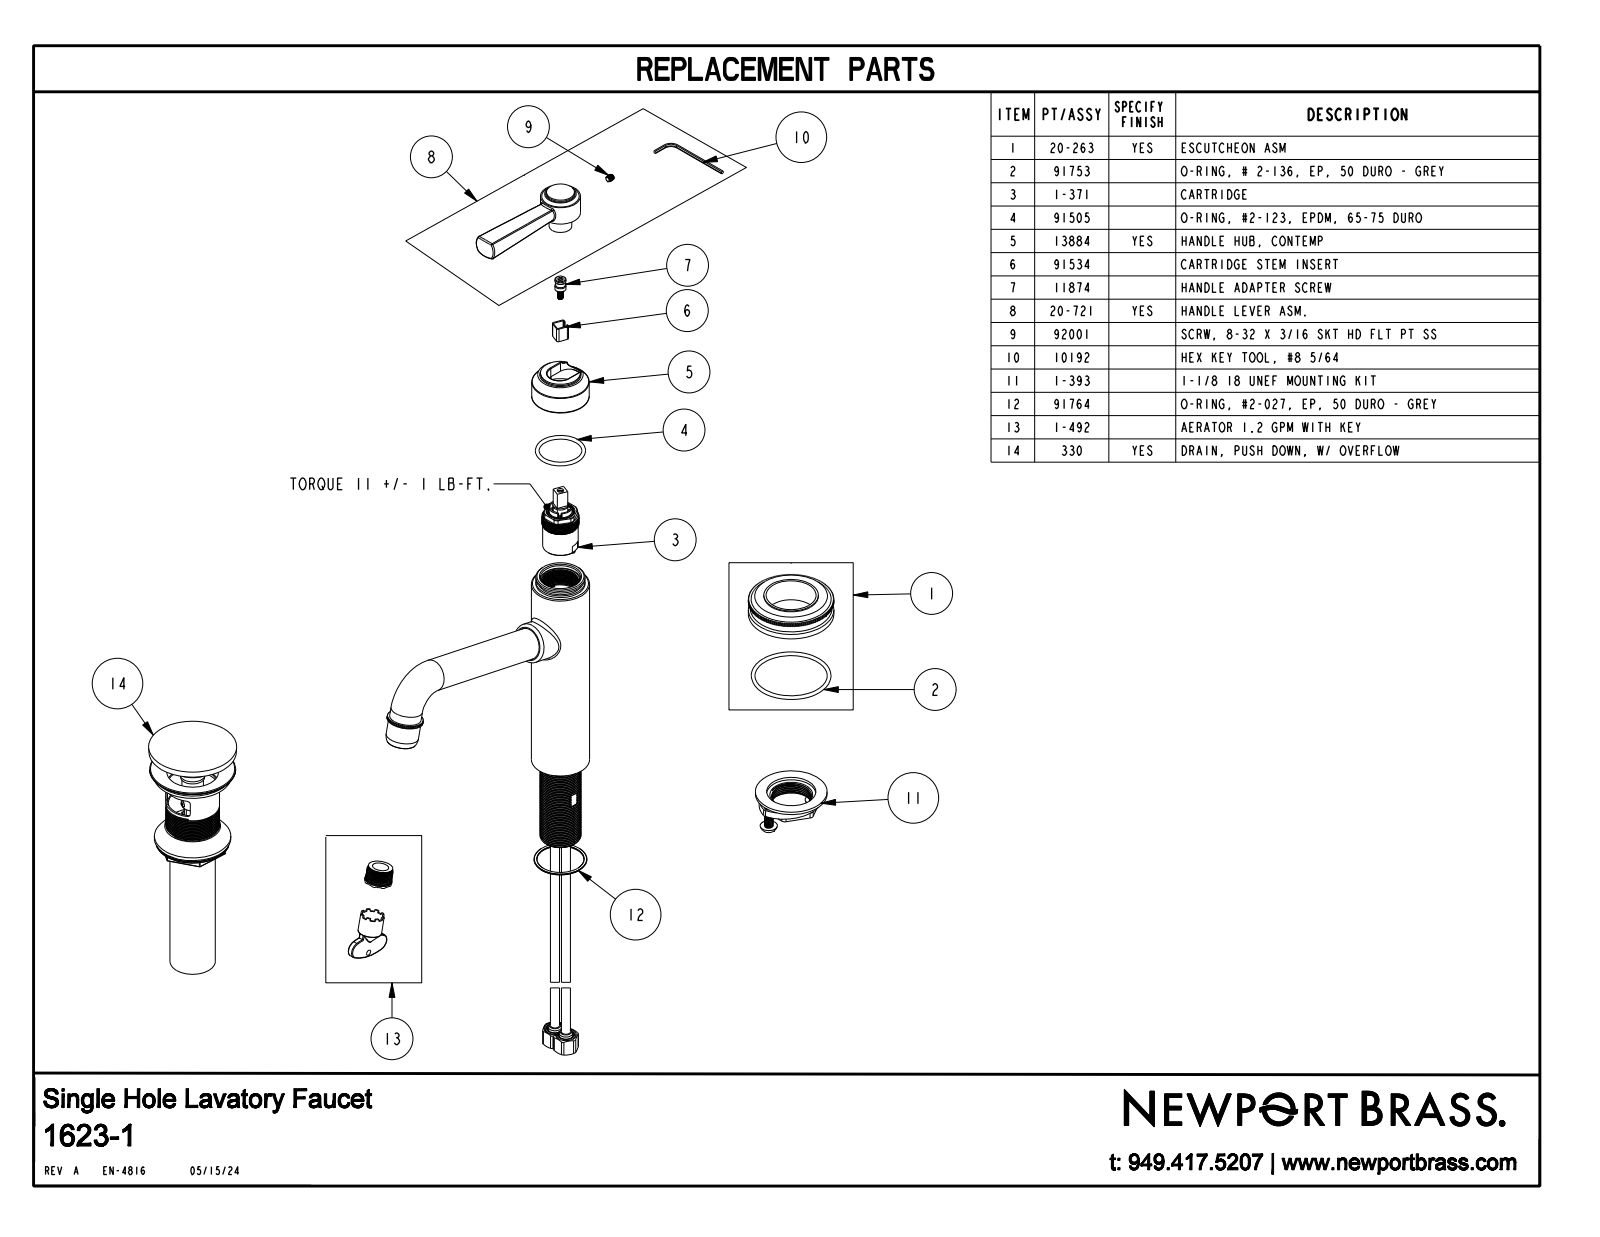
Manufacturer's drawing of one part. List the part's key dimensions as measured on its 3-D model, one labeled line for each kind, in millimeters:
Part name (STEP PRODUCT): 1623-1_SW0001
STEP written by: CREO PARAMETRIC BY PTC INC, 2023134 (CONFIG_CONTROL_DESIGN)
Units: millimetres
Bodies: 1 solid, 655 faces (370 planar, 209 cylindrical, 76 other)
Overall size (bounding box): 210.4 × 197.4 × 59.7
Volume: 348 400 mm³ · Surface area: 48 480 mm²
Round bosses / shafts (diameter × count): ⌀27.9 ×2, ⌀22.2 ×2, ⌀59.7 ×1, ⌀57.2 ×1, ⌀40.6 ×1, ⌀40.1 ×1, ⌀38.4 ×1, ⌀36.6 ×1
Partial cylindrical surfaces — rounded edges, fillets, slot ends (radius × count): R0.3 ×2, R0.5 ×2, R8.7 ×2, R12.7 ×1
Main face-to-face distances: 15.5, 2.5, 192.8, 177.3, 13, 179.9, 210.3, 197.4, 194.9, 17.5
